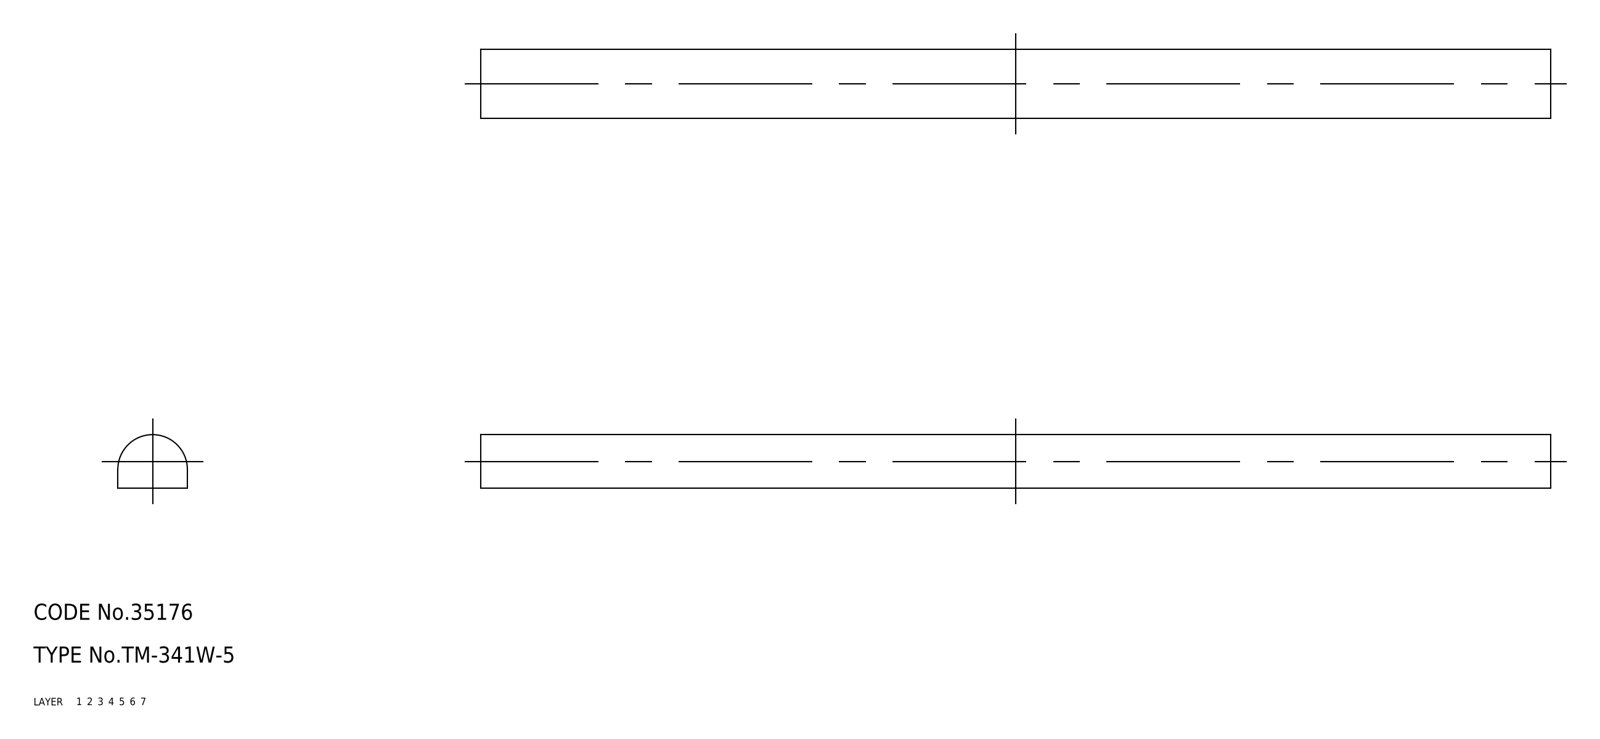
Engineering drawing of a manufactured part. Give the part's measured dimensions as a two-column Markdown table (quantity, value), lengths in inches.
| quantity | value |
| --- | --- |
| part name | rubber foam; TM_341W_5 |
| STEP written by | SolidWorks 2015 (AUTOMOTIVE_DESIGN) |
| units | inches |
| bodies | 1 solid, 6 faces (5 planar, 1 cylindrical, 0 other) |
| overall size | 7.874 × 0.512 × 0.394 |
| volume | 1.365 in³ |
| surface area | 12.88 in² |
| partial cylindrical surfaces (radius × count) | 0.256 × 1 |
| main face-to-face distances | 0.512, 7.874 |
